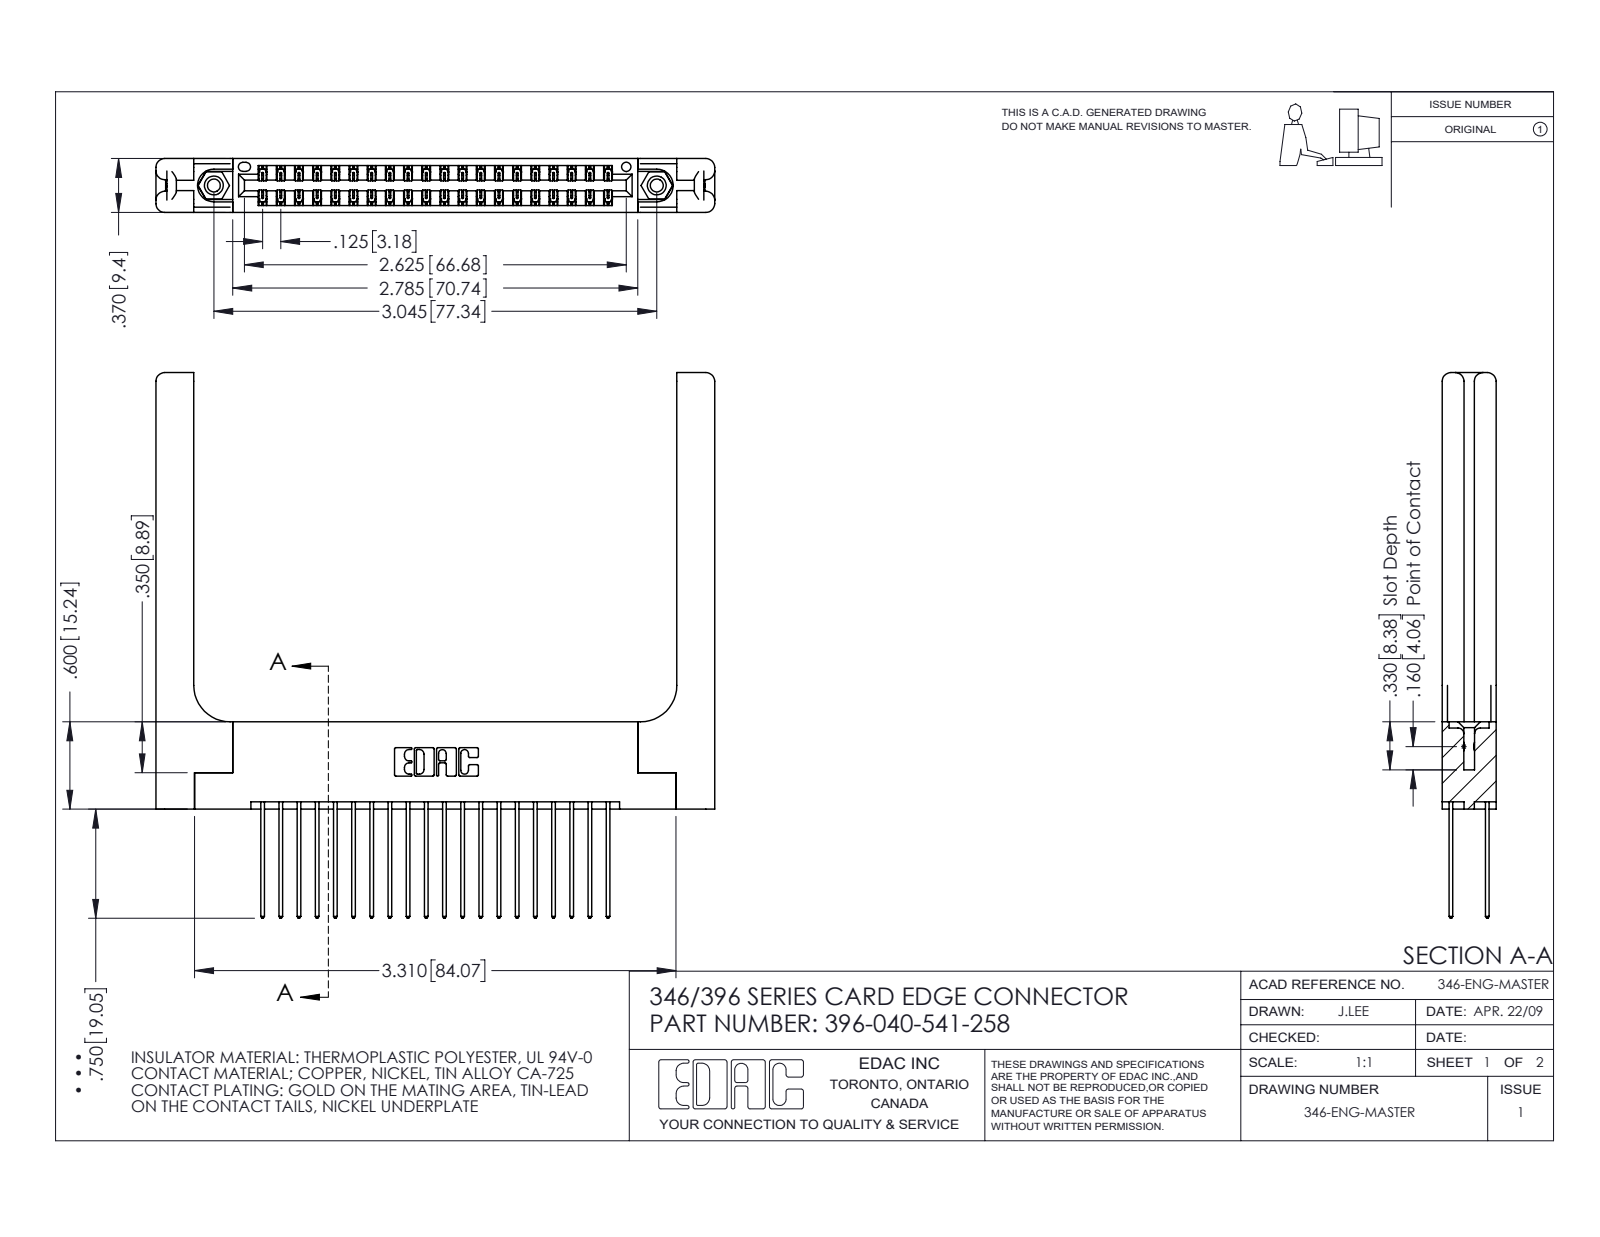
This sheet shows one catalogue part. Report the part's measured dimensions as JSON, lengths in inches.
{"part_name": "345-292-001_345-293-141; 346-220-058_345-220-058; 396-040-541-258; 346 Part_Flush Mounting Lugs - 0.156 Dia-TH (+1 more)", "step_written_by": "SolidWorks 2016 (CONFIG_CONTROL_DESIGN)", "units": "inches", "bodies": {"solids": 45, "faces": 2458, "planar": 1624, "cylindrical": 774, "other": 60}, "overall_size": [3.841, 3.75, 0.37], "volume_in3": 1.041, "surface_area_in2": 29.27, "round_holes": [[0.089, 2], [0.125, 2], [0.156, 2], [0.064, 1]], "round_bosses_or_shafts": [[0.155, 2]], "partial_cylinders_radius": [[0.006, 60], [0.01, 40], [0.01, 22], [0.06, 16], [0.007, 6], [0.031, 6], [0.026, 3], [0.014, 2]], "face_to_face_distances": [0.37, 0.072, 0.048, 0.322, 0.25, 0.15, 0.148, 0.025, 0.298, 0.275], "hole_center_spacings": [0.246, 2.837, 3.045]}
